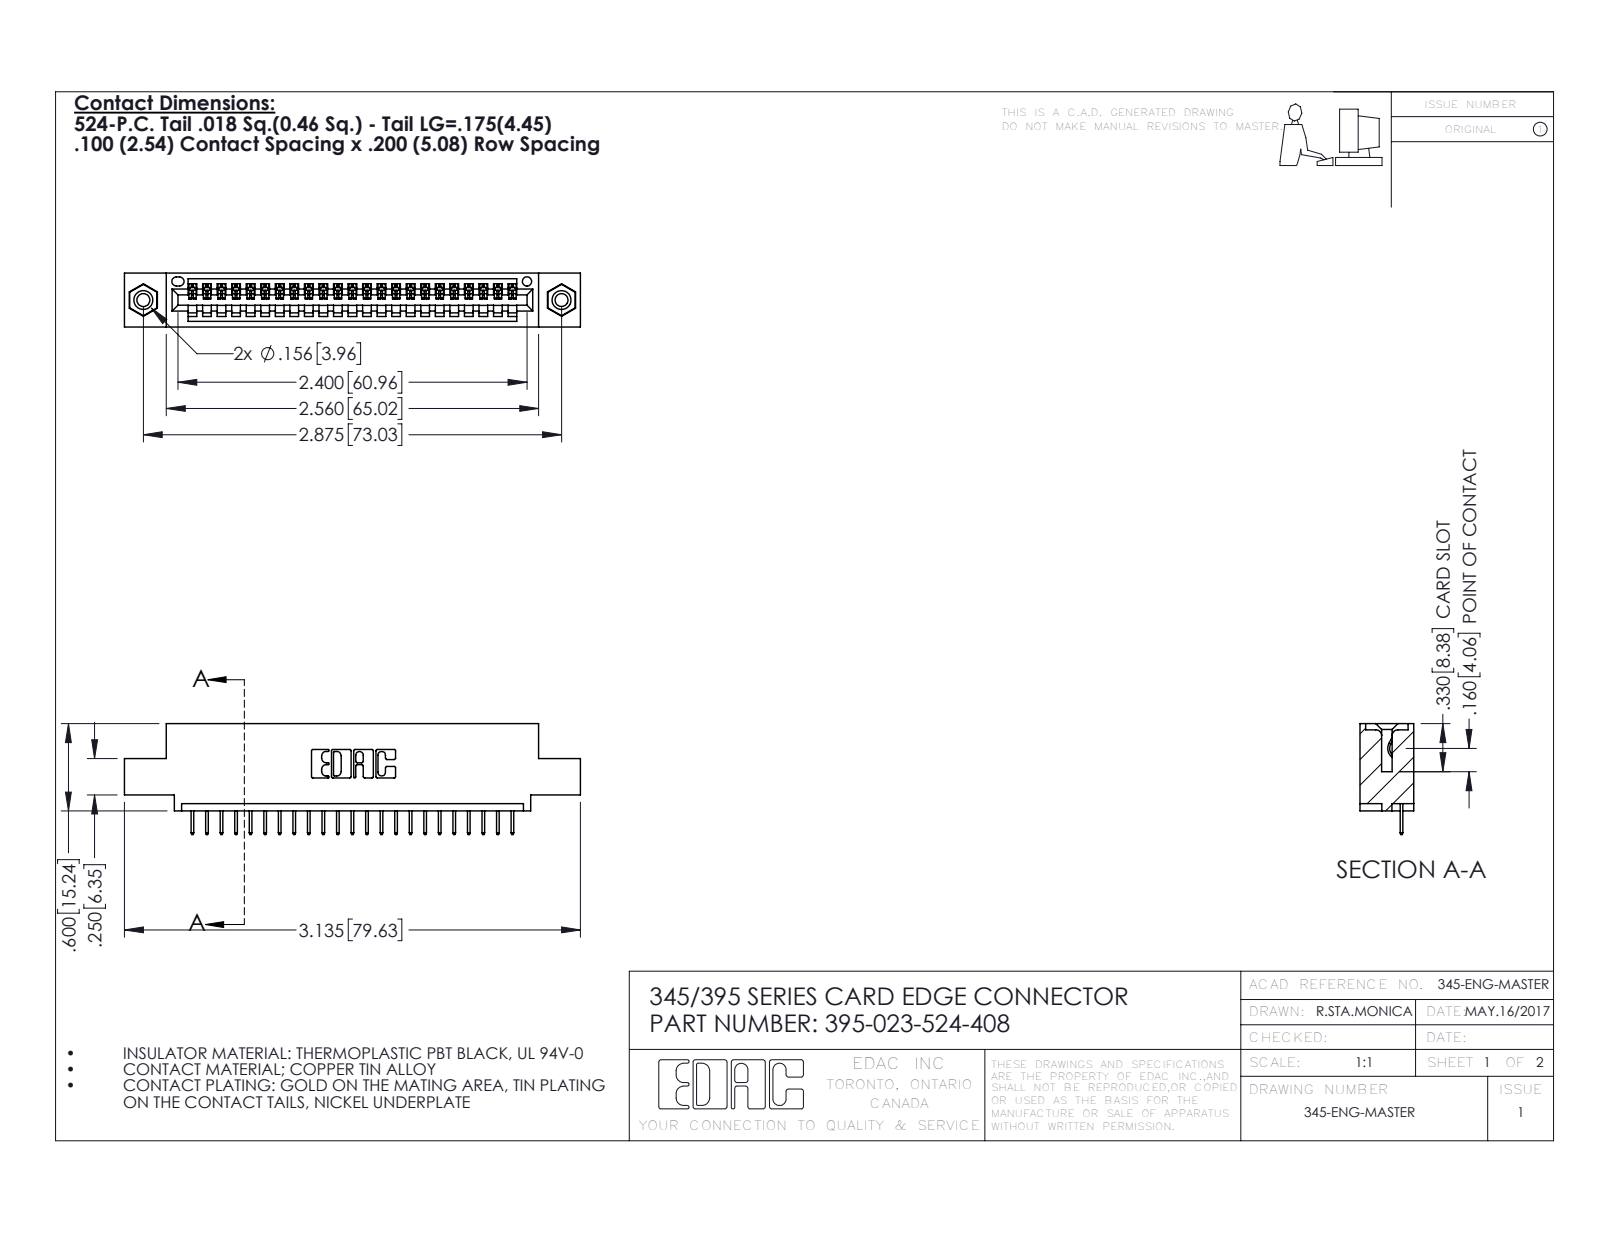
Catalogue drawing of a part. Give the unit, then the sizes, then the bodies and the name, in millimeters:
Units: millimetres
Overall size (bounding box): 79.6 × 19.4 × 9.4
Round holes (diameter × count): ⌀2.3 ×2, ⌀3.2 ×2, ⌀4 ×2, ⌀1.6 ×1
Round bosses / shafts (diameter × count): ⌀3.9 ×2
Partial cylindrical surfaces — rounded edges, fillets, slot ends (radius × count): R0.2 ×46, R0.3 ×22, R0.2 ×6, R0.8 ×6, R0.7 ×3, R0.8 ×2, R1 ×2, R0.4 ×1
Main face-to-face distances: 1.8, 7.6, 9.4, 5.1, 2.5, 6.9, 0.6, 5.7, 1.8, 3.8
Hole centre spacings: 6.9, 67.1, 73
Volume: 7 240 mm³ · Surface area: 9 168 mm²
Bodies: 26 solids, 1616 faces (1174 planar, 426 cylindrical, 16 other)
Part name (STEP PRODUCT): 345-292-001_345-293-124; 345-250-001_345-250-003-102; 345 Part_0.110 Offset - 0.156 Dia-TI; 395-023-524-408
STEP written by: SolidWorks 2016 (CONFIG_CONTROL_DESIGN)
